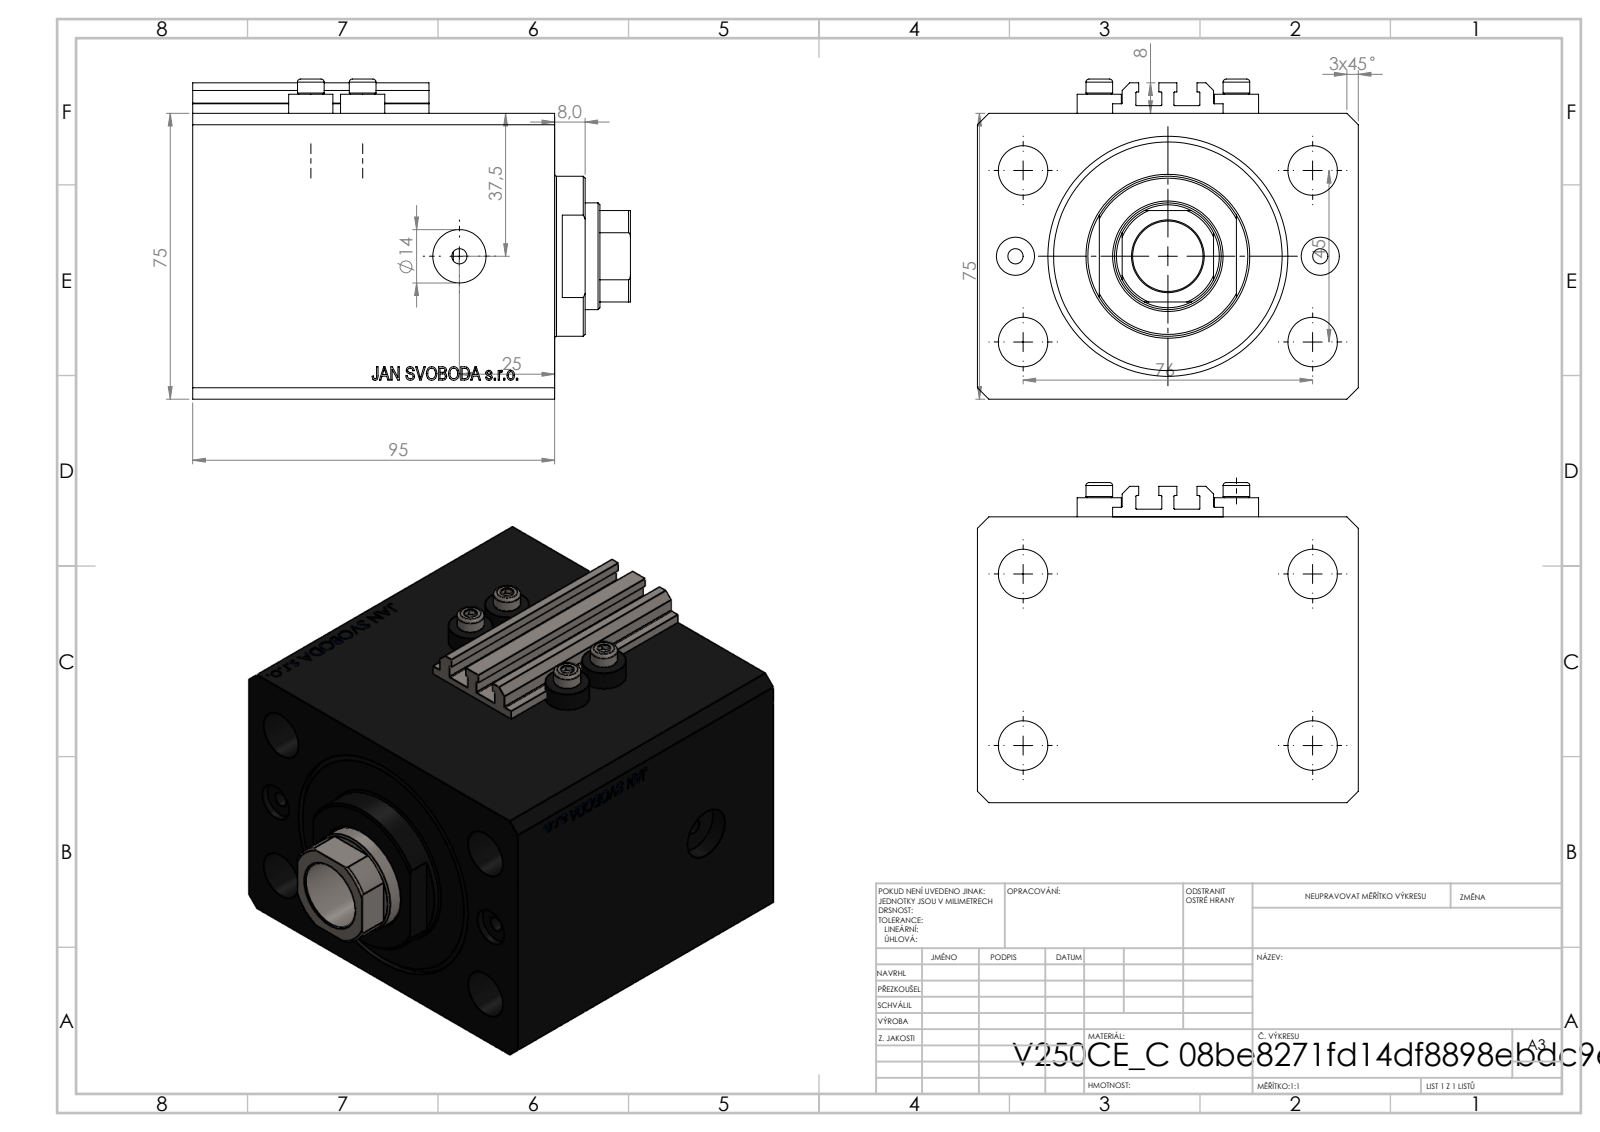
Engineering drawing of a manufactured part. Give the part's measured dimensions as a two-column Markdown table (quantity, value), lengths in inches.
| quantity | value |
| --- | --- |
| part name | V250CE_VC_C; V250CE_C_VCP; ALLEN BOLT V250CE; V250CE_C_Body |
| STEP written by | SolidWorks 2019 (CONFIG_CONTROL_DESIGN) |
| units | inches |
| bodies | 8 solids, 1034 faces (504 planar, 86 cylindrical, 444 other) |
| overall size | 4.524 × 3.937 × 3.307 |
| volume | 39.54 in³ |
| surface area | 184 in² |
| round holes (diameter × count) | 0.157 × 8, 0.512 × 4, 0.394 × 2, 0.551 × 2, 0.728 × 1, 1.102 × 1, 1.969 × 1, 2.48 × 1 |
| round bosses / shafts (diameter × count) | 0.457 × 4, 0.276 × 4, 1.654 × 1 |
| partial cylindrical surfaces (radius × count) | 0.008 × 10, 0.531 × 1 |
| main face-to-face distances | 2.953, 3.937, 3.74, 0.469, 3.272, 2.693, 2.224, 1.047, 1.906, 1.437 |
| hole center spacings | 0.889, 1.739, 3.196, 1.772, 0.535, 1.417, 1.515, 1.575 |
